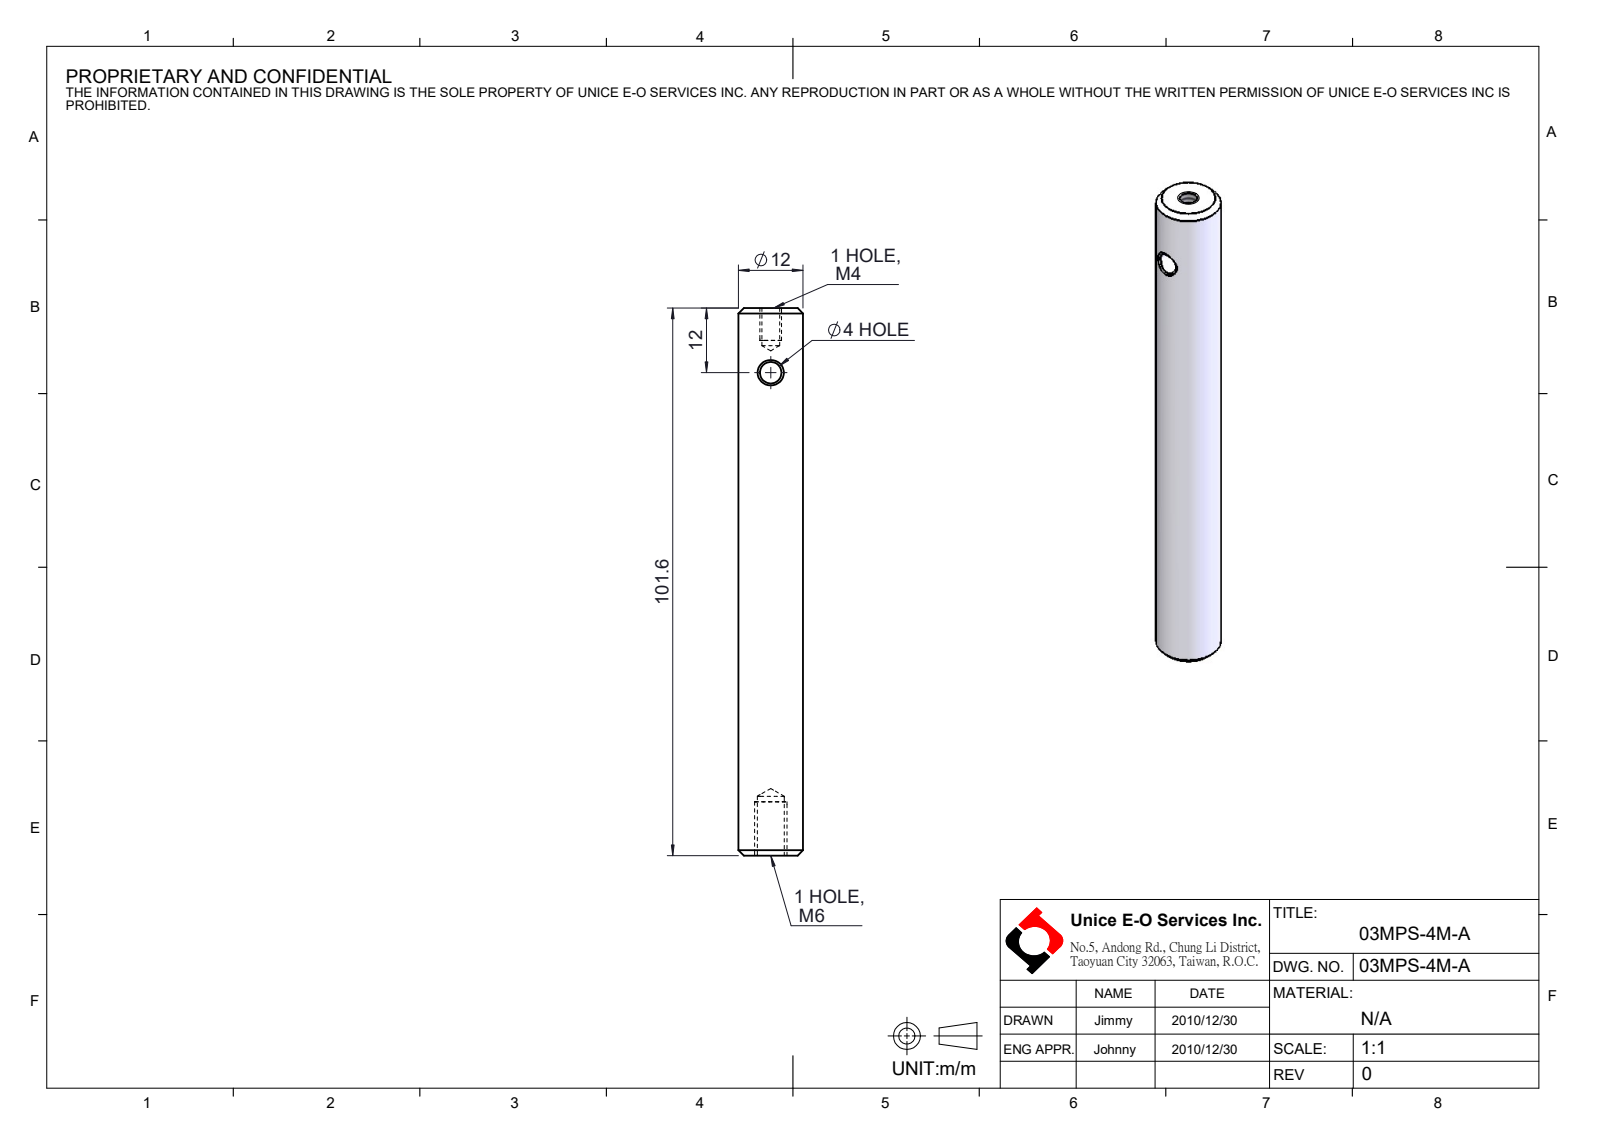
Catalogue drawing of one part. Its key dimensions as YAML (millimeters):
part_name: "03MPS-4M-A"
step_written_by: "SolidWorks 2016 (CONFIG_CONTROL_DESIGN)"
units: millimeters
bodies: {solids: 1, faces: 22, planar: 2, cylindrical: 8, other: 12}
overall_size: [101.6, 12, 12]
volume: 11017
surface_area: 4374
round_holes:
  - {diameter: 3.3, count: 1}
  - {diameter: 4, count: 1}
  - {diameter: 5, count: 1}
round_bosses_or_shafts:
  - {diameter: 12, count: 1}
face_to_face_distances: [101.6]
